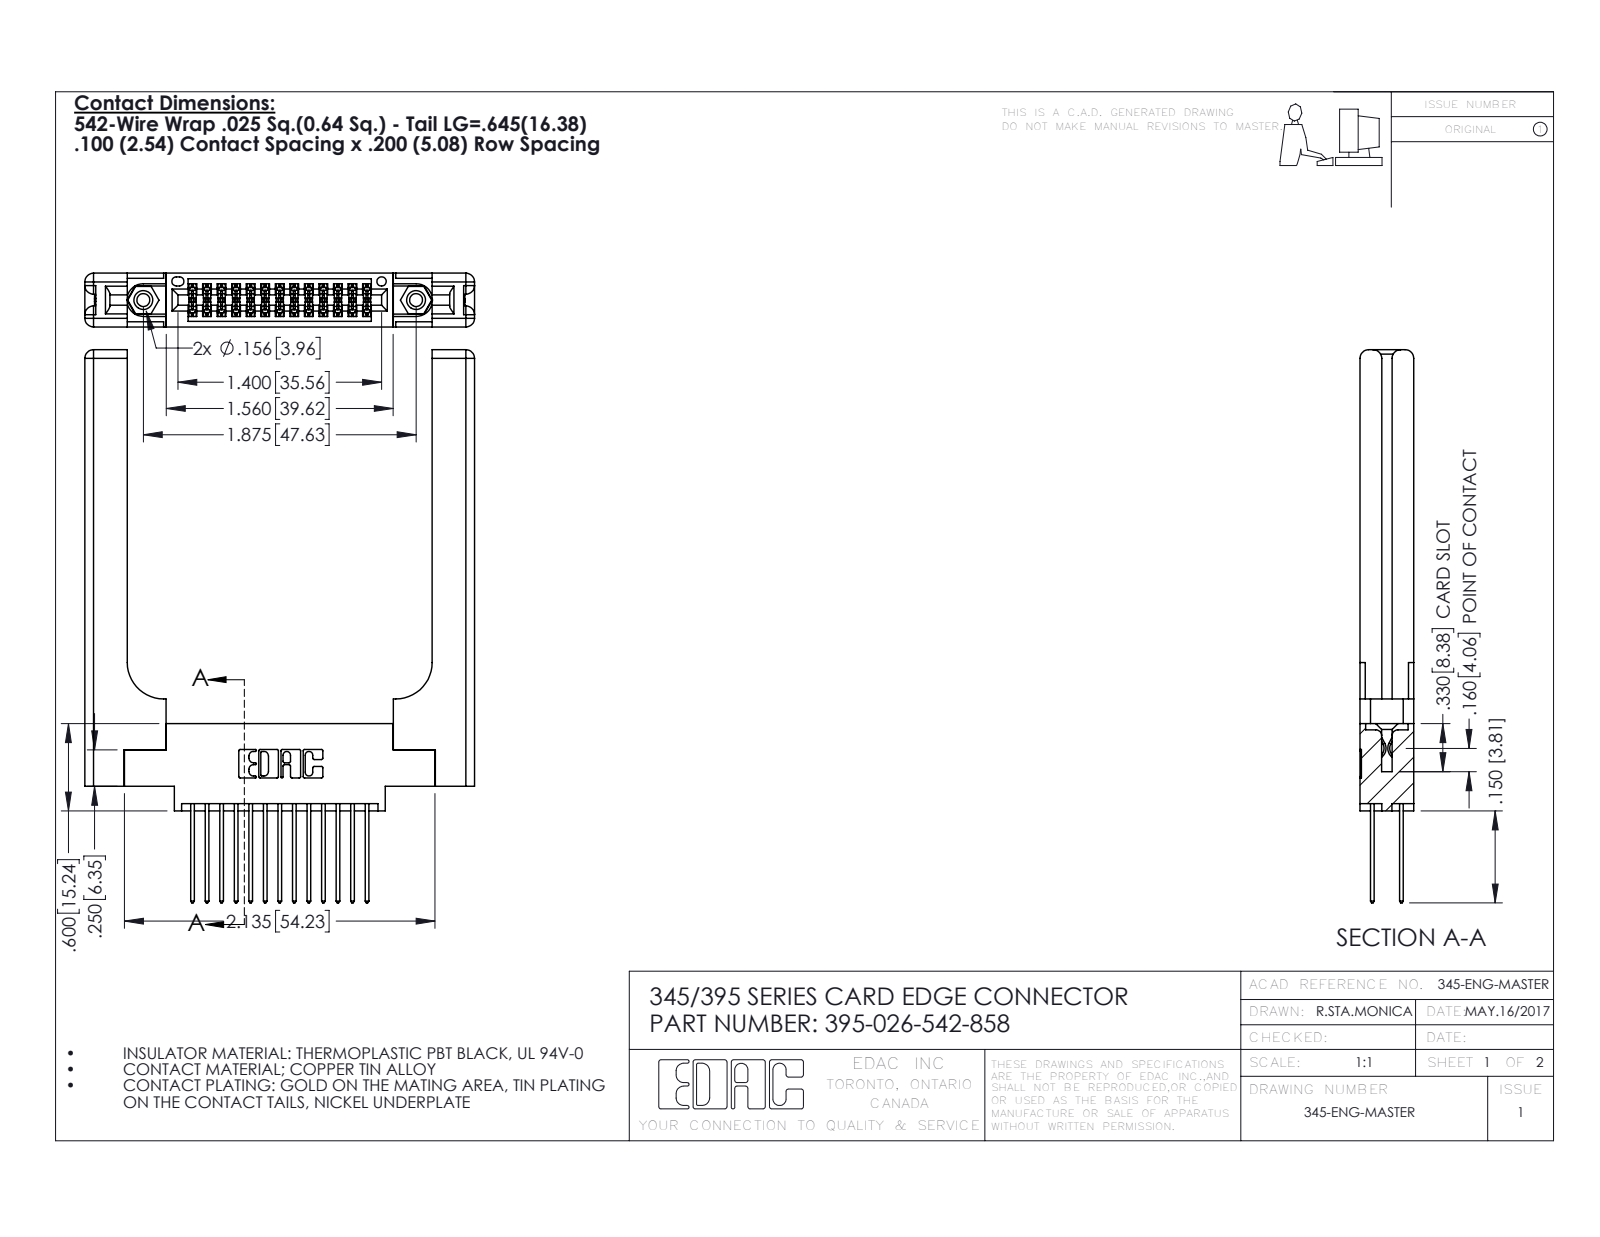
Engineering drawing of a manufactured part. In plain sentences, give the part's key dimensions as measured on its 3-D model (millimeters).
The part is named "345 Part_0.170 Offset - 0.156 Dia-TH; 345-292-001_345-293-142; 395-026-542-858; 345-250-001_345-250-001-102 (+1 more)". Its 3-D file was written by "SolidWorks 2016 (CONFIG_CONTROL_DESIGN)". It is 31 solids with 1686 faces: 1090 planar, 536 cylindrical and 60 other. Overall it measures 96.6 by 68 by 9.4 millimeters. Its volume is 14 800 cubic millimeters and its surface area 14 590 square millimeters. Round holes: 2 of diameter 2.3, 2 of diameter 3.2, 2 of diameter 4, 1 of diameter 1.6. Round bosses or shafts: 2 of diameter 3.9. Partial cylindrical surfaces (rounded edges, fillets, slot ends): 39 of radius 0.2, 26 of radius 0.3, 22 of radius 0.3, 16 of radius 1.5, 6 of radius 0.2, 6 of radius 0.8, 3 of radius 0.7, 2 of radius 0.4. The main face-to-face distances are 9.4, 1.8, 7.6, 3.8, 3.8, 2, 5.6, 3.1, 2.5, 6.9. The hole center spacings are 6.9, 41.7, 47.6.
